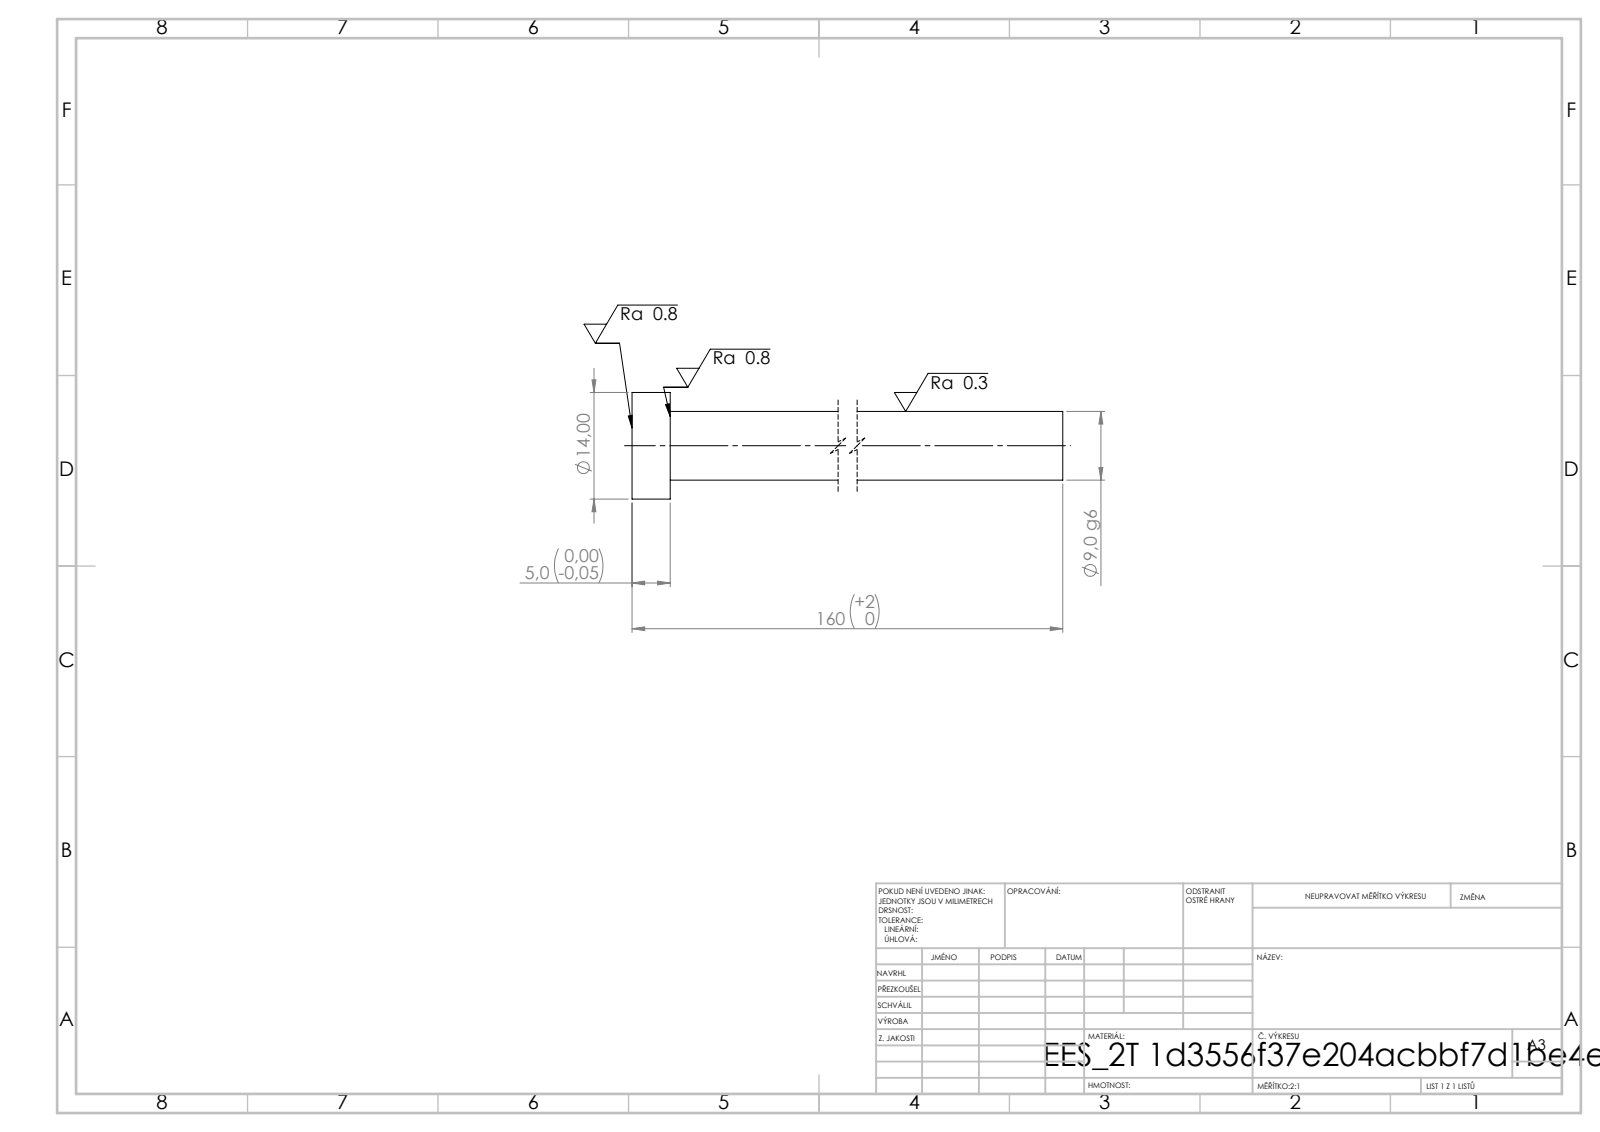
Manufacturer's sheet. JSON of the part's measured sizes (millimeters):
{"step_written_by": "SolidWorks 2019 (CONFIG_CONTROL_DESIGN)", "units": "millimeters", "bodies": {"solids": 1, "faces": 7, "planar": 3, "cylindrical": 4, "other": 0}, "overall_size": [160, 14, 14], "volume_mm3": 10630, "surface_area_mm2": 4910, "round_bosses_or_shafts": [[14, 1], [9, 1]], "face_to_face_distances": [5, 160, 155]}
